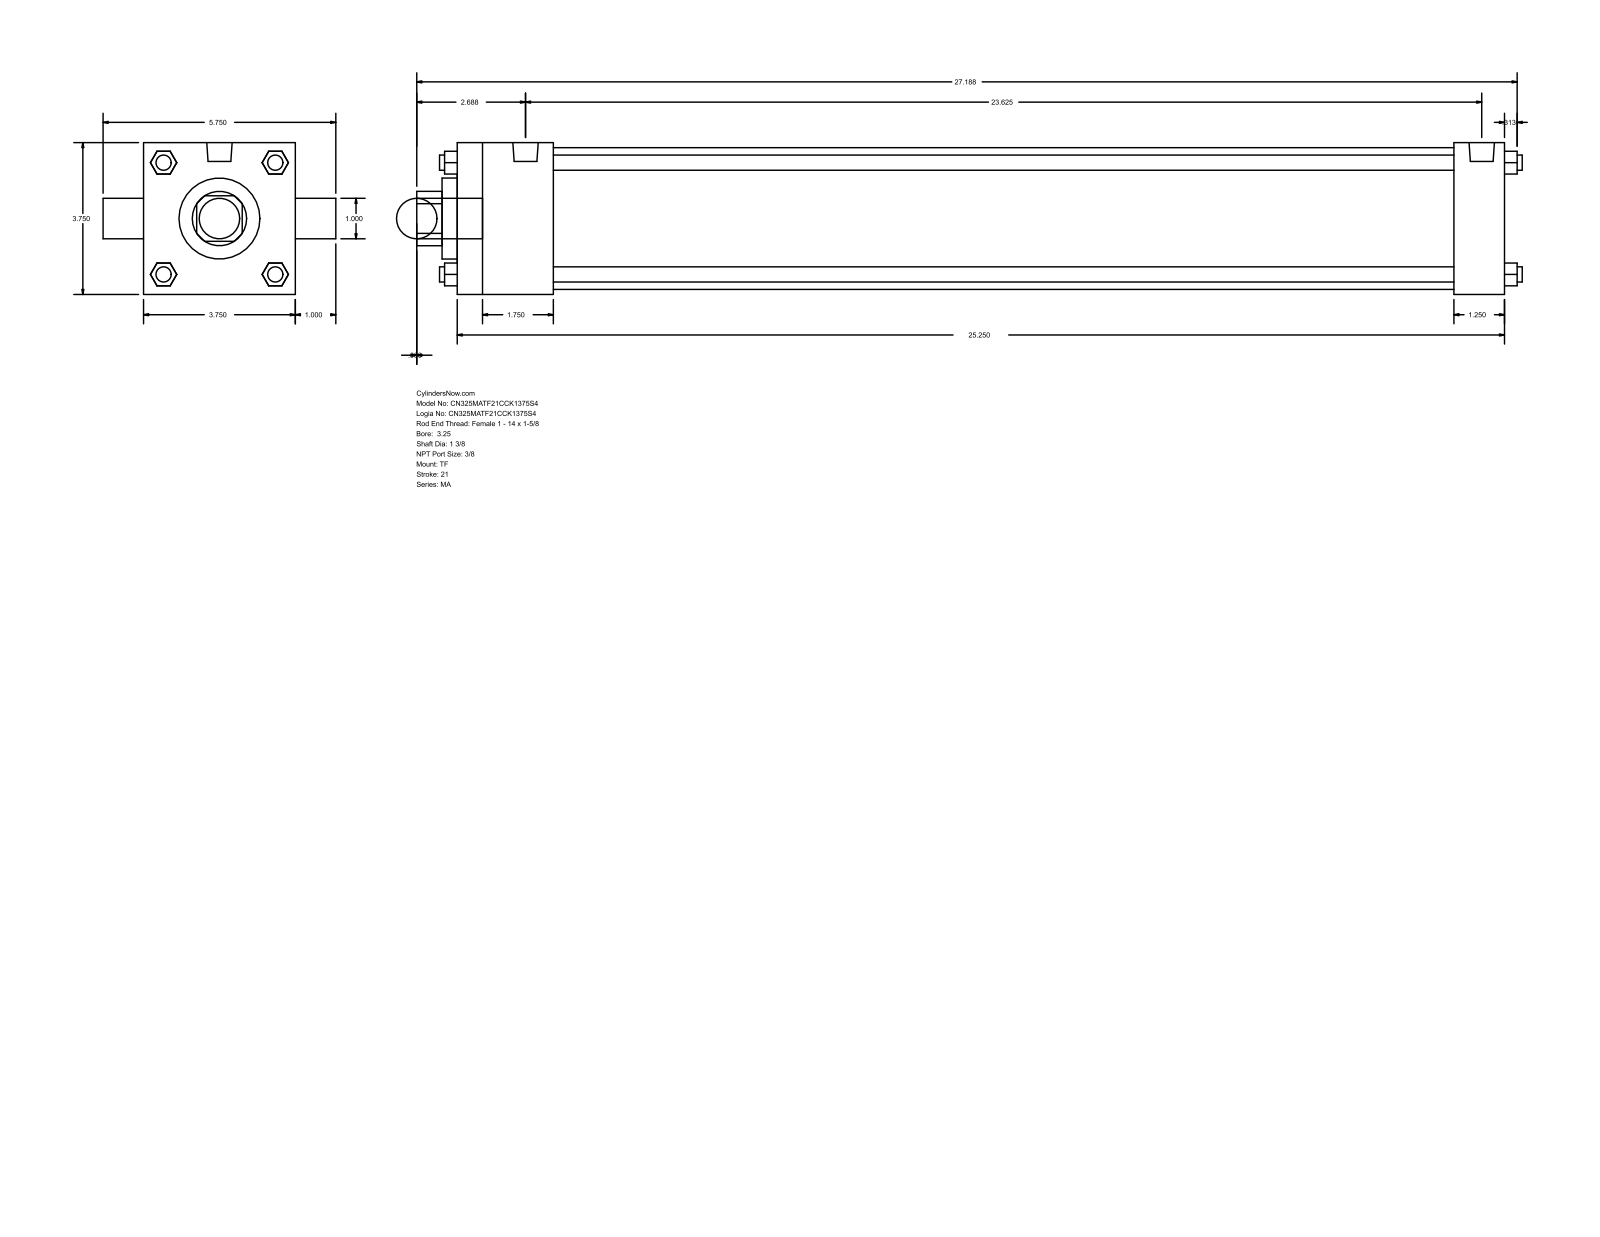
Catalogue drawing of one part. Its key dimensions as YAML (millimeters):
part_name: "MA_TF__0325_1.375"
step_written_by: "GSSL Pune (CONFIG_CONTROL_DESIGN)"
units: millimeters
bodies: {solids: 0, faces: 120, planar: 92, cylindrical: 28, other: 0}
overall_size: [693.74, 146.05, 95.25]
round_holes:
  - {diameter: 25.4, count: 1}
  - {diameter: 34.92, count: 1}
  - {diameter: 50.8, count: 1}
  - {diameter: 88.9, count: 1}
round_bosses_or_shafts:
  - {diameter: 9.53, count: 4}
  - {diameter: 11.11, count: 3}
  - {diameter: 15.93, count: 2}
  - {diameter: 25.4, count: 1}
partial_cylinders:
  - {radius: 17.06, count: 1}
face_to_face_distances: [95.24, 657.22, 60.32, 625.48, 565.16, 596.9, 31.74, 9.52, 69.84, 635]
